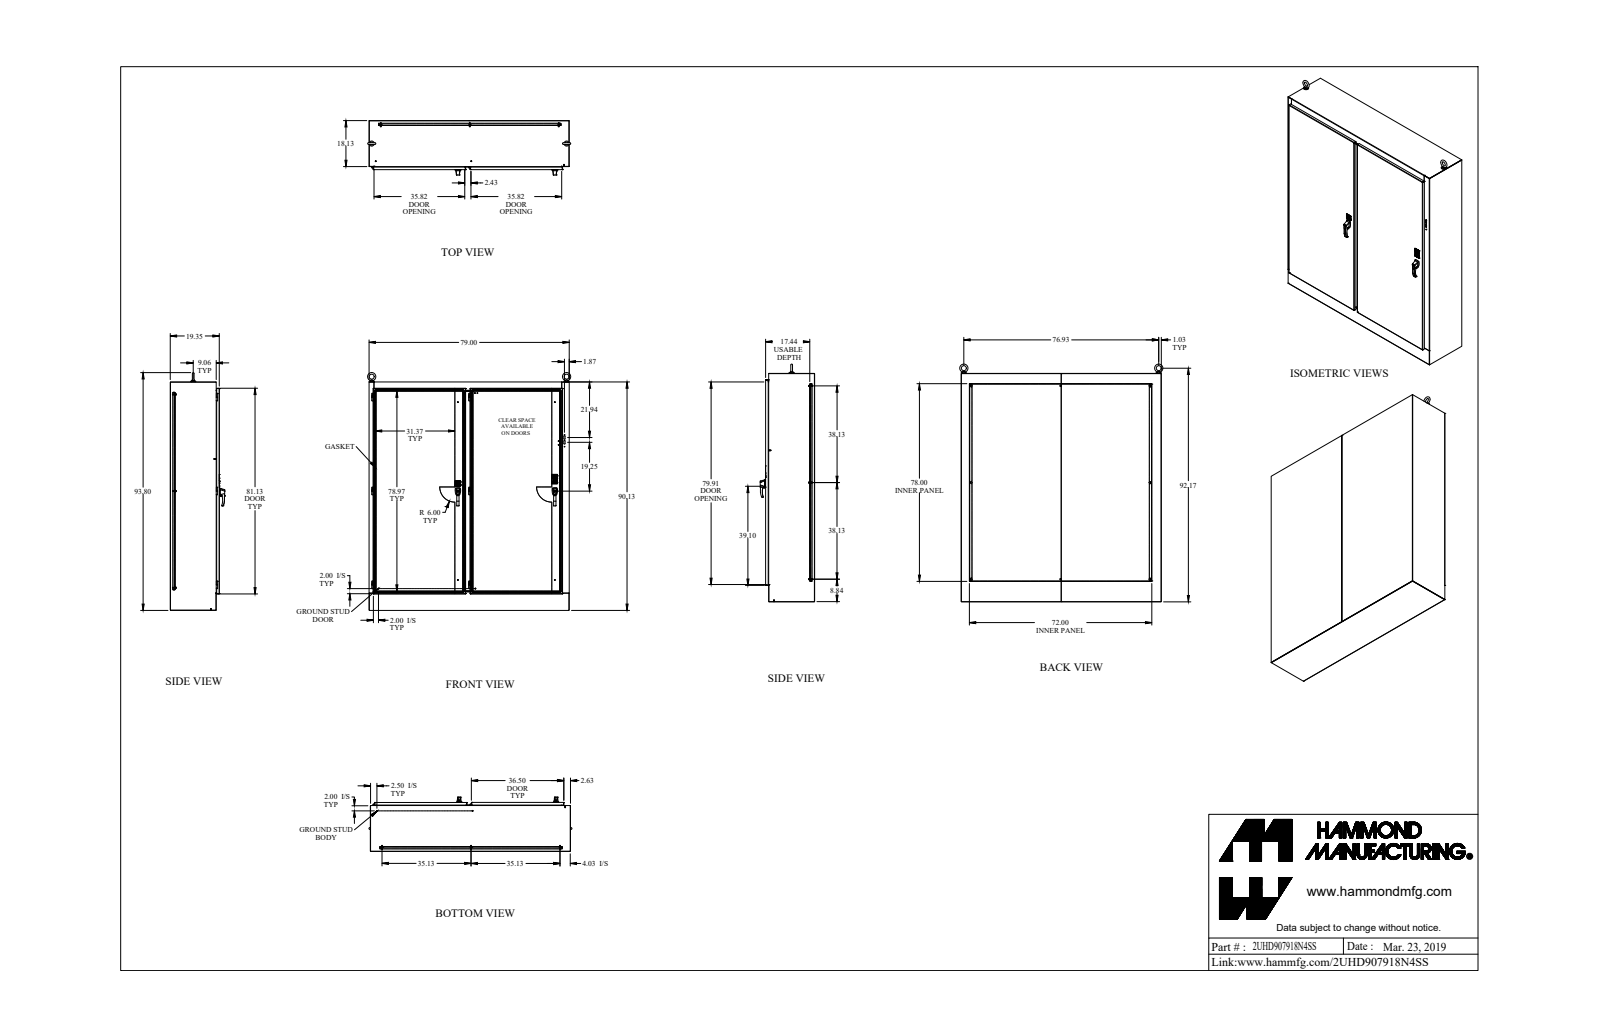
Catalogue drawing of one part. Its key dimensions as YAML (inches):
part_name: "2UHD907918N4SS"
step_written_by: "SolidWorks 2018 (AUTOMOTIVE_DESIGN)"
units: inches
bodies: {solids: 223, faces: 3338, planar: 1961, cylindrical: 990, other: 387}
overall_size: [93.799, 80.182, 21.466]
volume: 5408
surface_area: 61936
round_holes:
  - {diameter: 0.25, count: 14}
  - {diameter: 0.196, count: 13}
  - {diameter: 0.281, count: 9}
  - {diameter: 0.307, count: 9}
  - {diameter: 0.35, count: 8}
  - {diameter: 0.255, count: 6}
  - {diameter: 0.257, count: 6}
  - {diameter: 0.313, count: 6}
  - {diameter: 0.201, count: 5}
  - {diameter: 0.313, count: 5}
  - {diameter: 0.445, count: 5}
  - {diameter: 0.156, count: 4}
round_bosses_or_shafts:
  - {diameter: 0.25, count: 18}
  - {diameter: 1, count: 12}
  - {diameter: 0.65, count: 9}
  - {diameter: 0.375, count: 9}
  - {diameter: 0.332, count: 8}
  - {diameter: 0.75, count: 6}
  - {diameter: 0.625, count: 6}
  - {diameter: 0.5, count: 6}
partial_cylinders:
  - {radius: 0.125, count: 67}
  - {radius: 0.5, count: 42}
  - {radius: 0.048, count: 34}
  - {radius: 0.143, count: 34}
  - {radius: 0.017, count: 32}
  - {radius: 0.06, count: 31}
  - {radius: 0.03, count: 28}
  - {radius: 0.25, count: 26}
face_to_face_distances: [0.095, 0.072, 17.461, 19.368, 19.273, 1.907, 1.812, 1.741, 1.835, 17.533]
hole_center_spacings: [38.25, 1, 1.287, 1.72, 3.43, 33.937, 36.188, 38.267]
